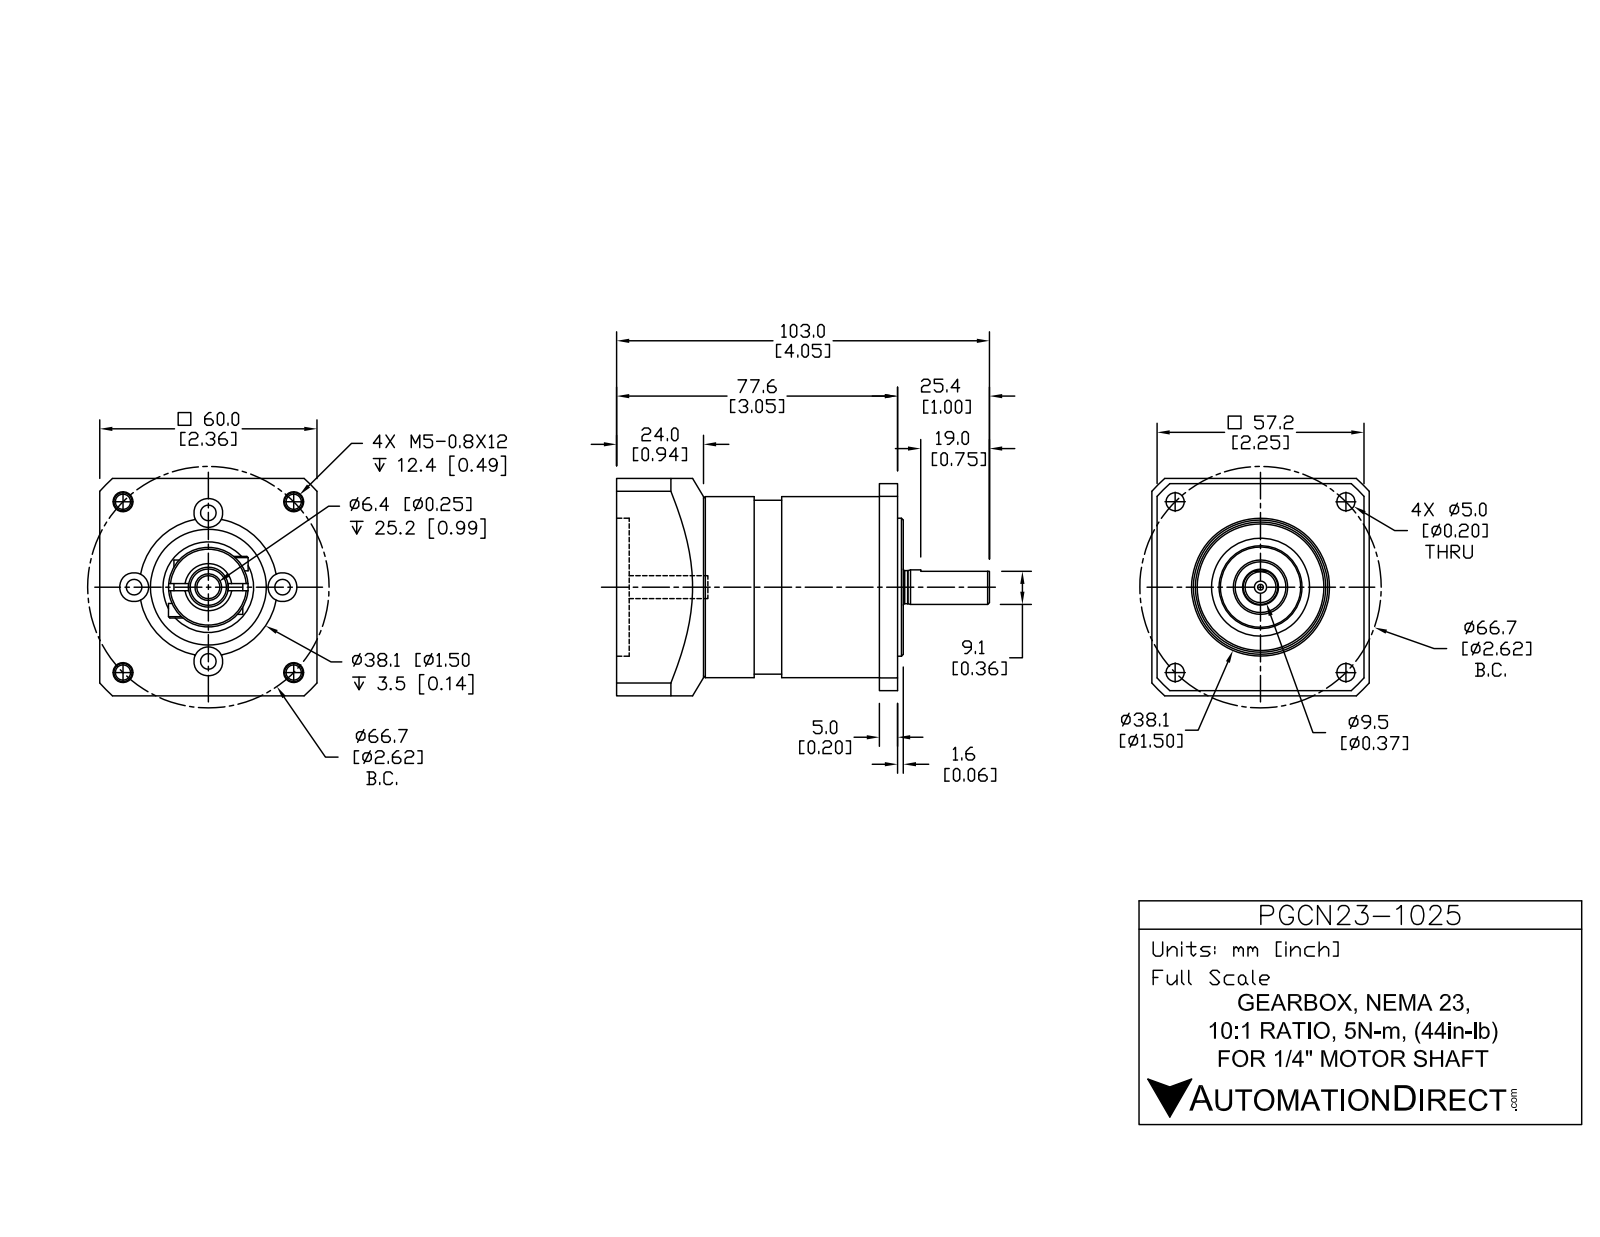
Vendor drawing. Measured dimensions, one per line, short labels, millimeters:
name: N23-F03_1; PGCN23-1025; Bushing_.25x11x14.9_1; PE-N23-I 11mm Input_1
written by: SolidWorks 2014 (AUTOMOTIVE_DESIGN)
unit: mm
bodies: 3 solids, 251 faces (69 planar, 114 cylindrical, 68 other)
size: 103 × 60 × 60
volume: 171 400 mm³; area: 36 120 mm²
holes: 4× ⌀4.2, 4× ⌀4.3, 4× ⌀5, 4× ⌀8, 2× ⌀4, 2× ⌀9, 1× ⌀1.6, 1× ⌀6.4, 1× ⌀11, 1× ⌀25, 1× ⌀27.1, 1× ⌀32
bosses: 2× ⌀7, 1× ⌀50, 1× ⌀48, 1× ⌀22.9, 1× ⌀22.2, 1× ⌀22, 1× ⌀15, 1× ⌀9.5
rounds: 2× R4, 1× R38, 1× R40
face distances: 77.6, 60, 53.6, 24, 5, 48.6, 72.6, 3, 1.4, 58.6
hole spacings: 23.8, 50, 20.5, 29, 33.3, 47.1, 1.3, 15
